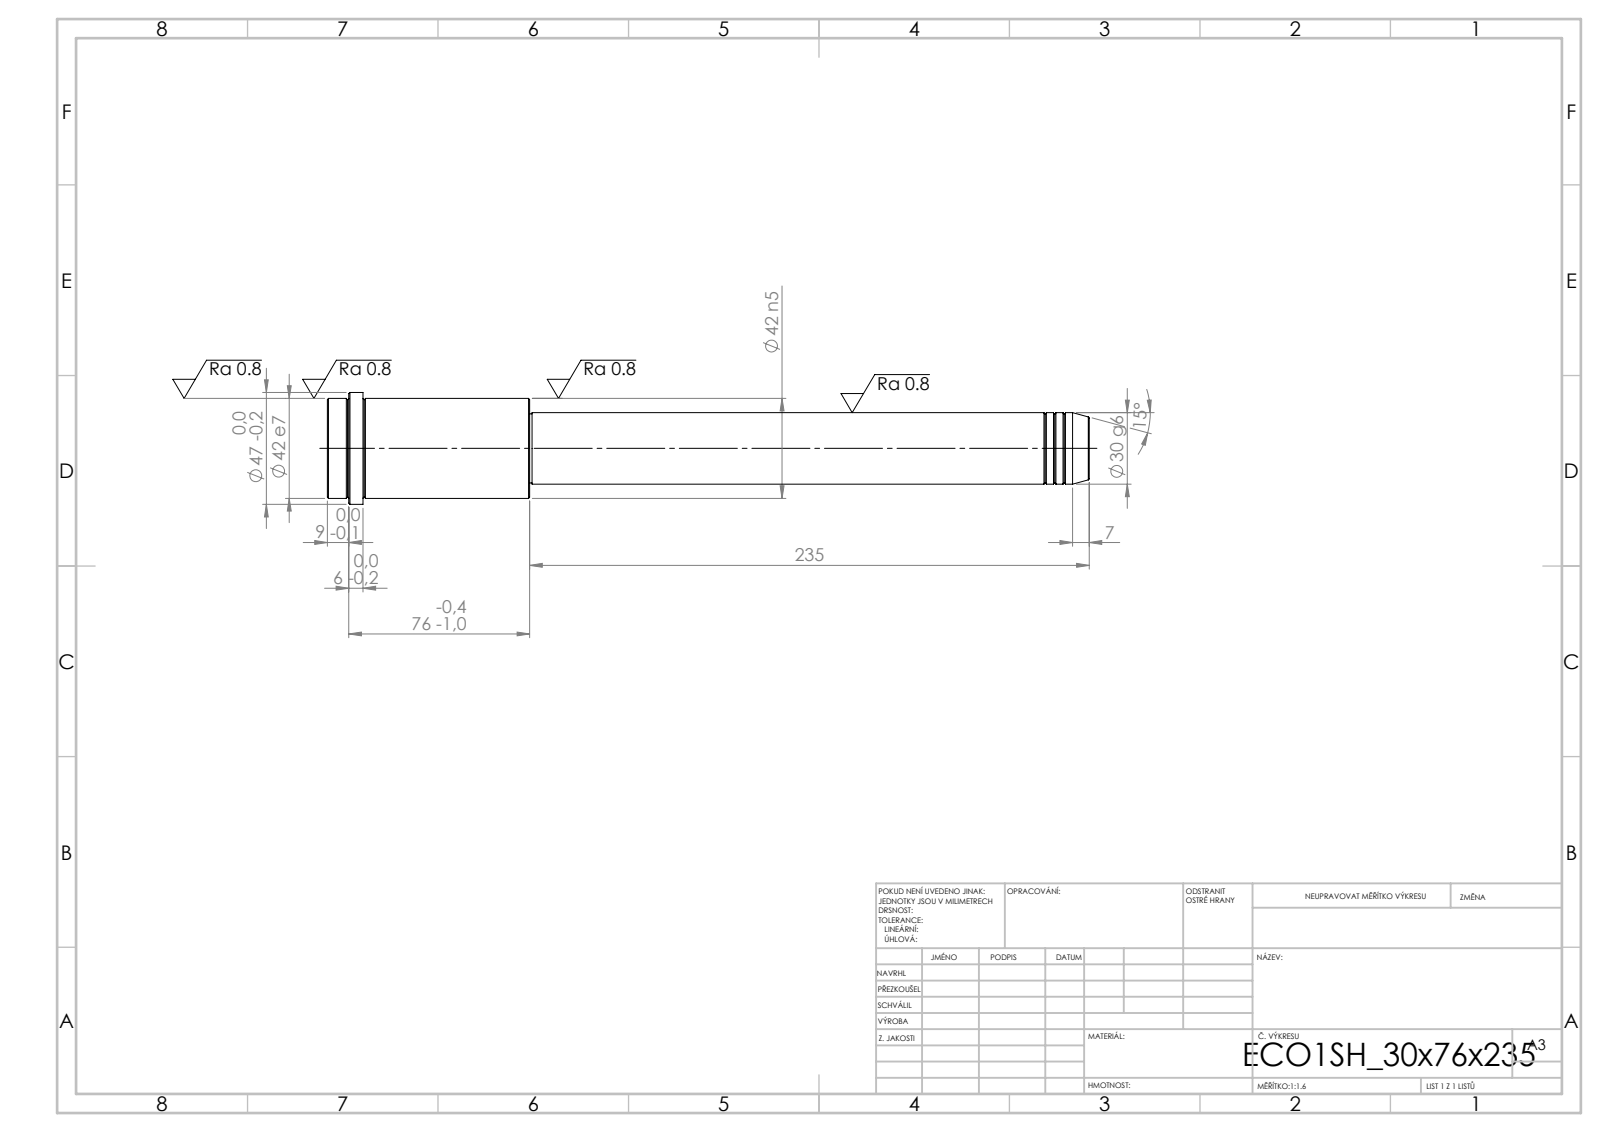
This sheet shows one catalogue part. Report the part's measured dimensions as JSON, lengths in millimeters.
{"step_written_by": "SolidWorks 2019 (CONFIG_CONTROL_DESIGN)", "units": "millimeters", "bodies": {"solids": 1, "faces": 52, "planar": 6, "cylindrical": 16, "other": 30}, "overall_size": [320, 47, 47], "volume_mm3": 285067, "surface_area_mm2": 36998, "round_bosses_or_shafts": [[47, 1], [42, 1], [30, 1], [29, 1]], "face_to_face_distances": [85, 235, 320, 305, 70, 15, 311, 76, 6, 9]}
